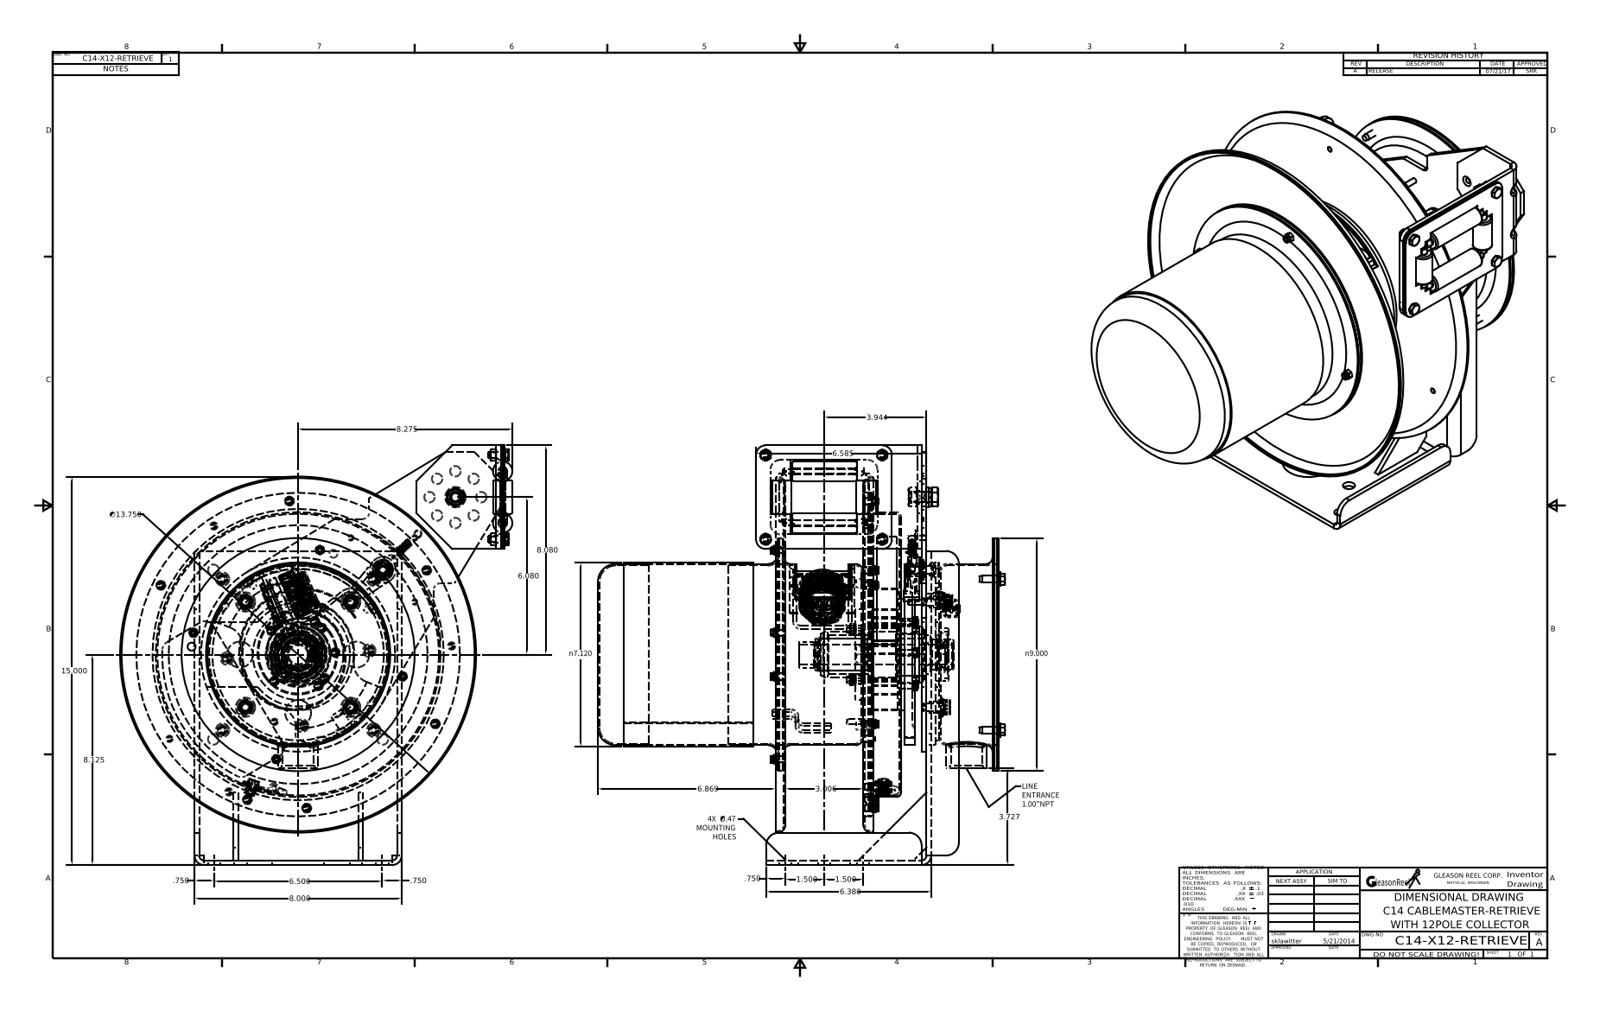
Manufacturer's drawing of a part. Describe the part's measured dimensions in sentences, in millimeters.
The part is named "C14-X12-RETRIEVE (SW)". Its 3-D file was written by "Autodesk Inventor 2016 (AUTOMOTIVE_DESIGN)". It is 159 solids with 3183 faces: 1260 planar, 1033 cylindrical and 890 other. Overall it measures 411.61 by 399.4 by 384.81 millimeters. Its volume is 2 765 000 cubic millimeters and its surface area 2 377 000 square millimeters. Round holes: 26 of diameter 6.35, 24 of diameter 5, 19 of diameter 4.13, 13 of diameter 10.31, 12 of diameter 5.56, 8 of diameter 5.41, 8 of diameter 10.67, 6 of diameter 11.94, 6 of diameter 25.4, 5 of diameter 4.92, 5 of diameter 7.14, 5 of diameter 7.98. Round bosses or shafts: 24 of diameter 5, 11 of diameter 6.8, 7 of diameter 10, 6 of diameter 6, 5 of diameter 12.7, 5 of diameter 11.6, 5 of diameter 8, 4 of diameter 19.05. Partial cylindrical surfaces (rounded edges, fillets, slot ends): 67 of radius 0.76, 64 of radius 0.24, 58 of radius 0.38, 18 of radius 1.98, 16 of radius 0.16, 12 of radius 1.52, 8 of radius 6.35, 8 of radius 9.53. The main face-to-face distances are 1.52, 3.17, 6.19, 30.93, 126.76, 4.69, 1.5, 4.67, 4.54, 84.04. The hole center spacings are 19.44, 25.4, 31.75, 35.92, 46.93, 51.91, 51.93, 76.
